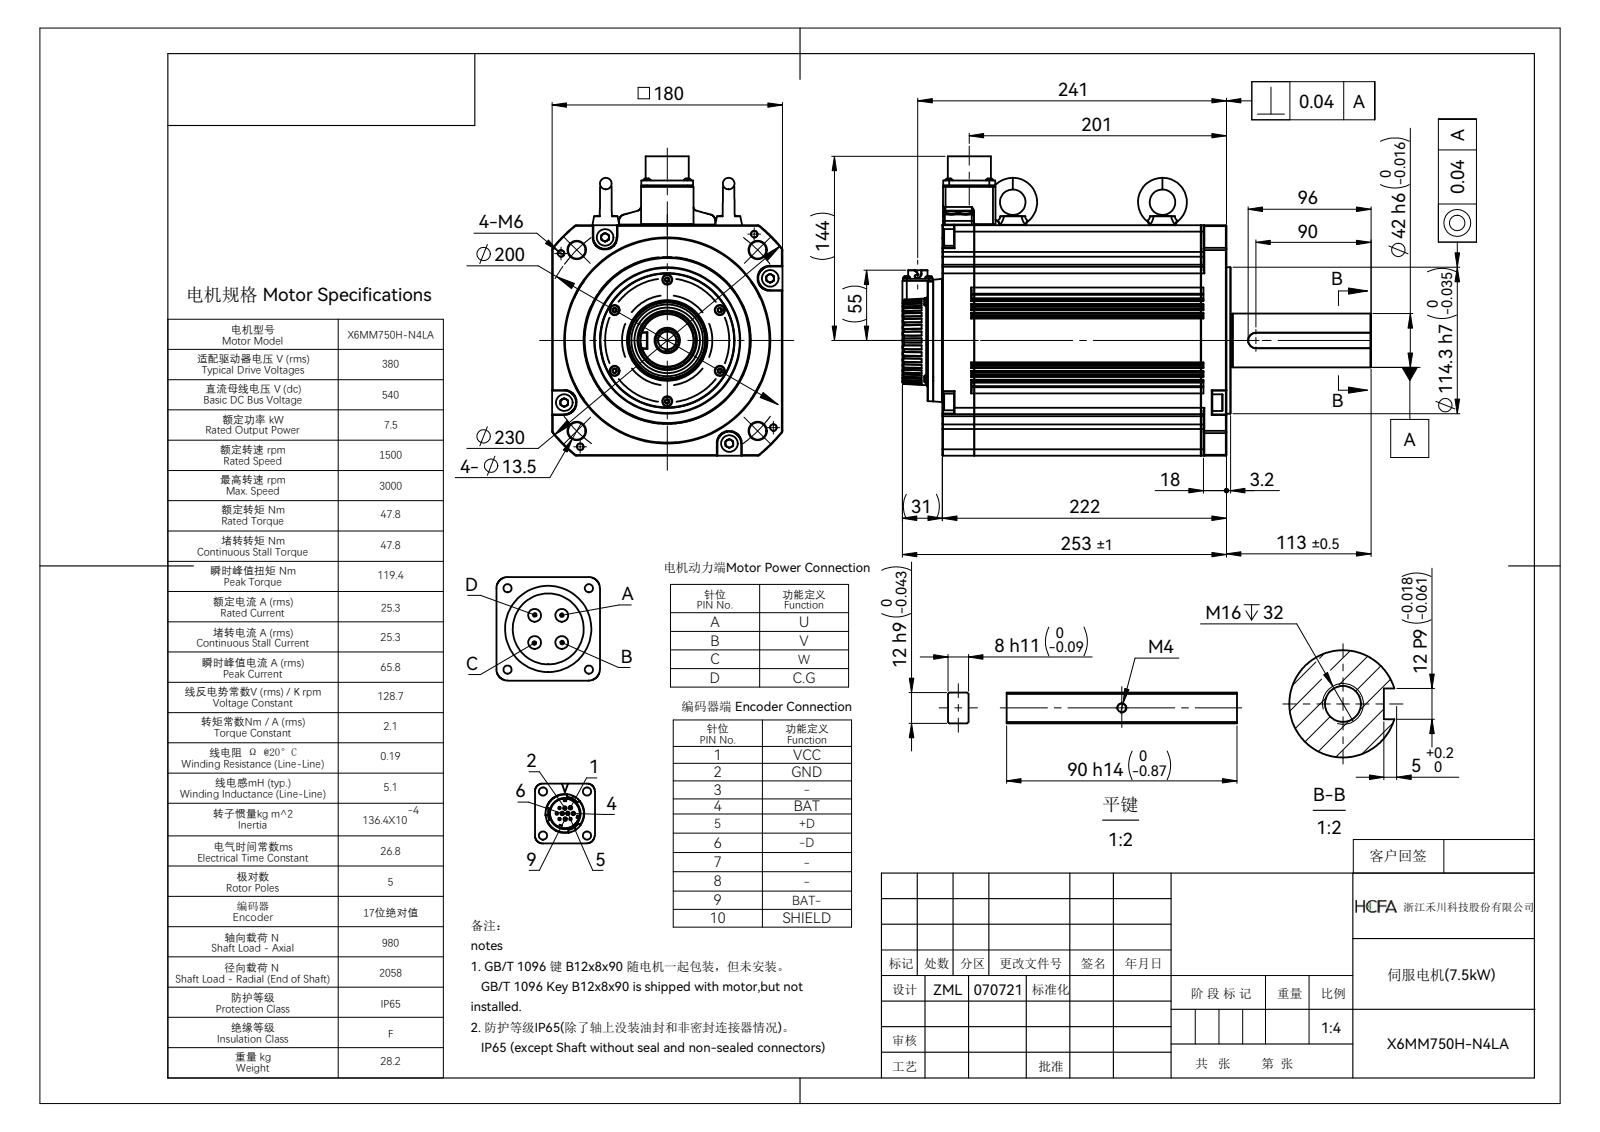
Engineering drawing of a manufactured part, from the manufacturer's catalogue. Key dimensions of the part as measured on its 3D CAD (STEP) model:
Part name (STEP PRODUCT): SV-X6MM750H-N4LA
STEP written by: SolidWorks 2016 (CONFIG_CONTROL_DESIGN)
Units: millimetres
Bodies: 1 solid, 2223 faces (763 planar, 831 cylindrical, 629 other)
Overall size (bounding box): 366.2 × 233.9 × 180
Volume: 6 642 000 mm³ · Surface area: 297 222 mm²
Round holes (diameter × count): ⌀13.5 ×4, ⌀2.5 ×2, ⌀11.6 ×1, ⌀11.8 ×1, ⌀14 ×1, ⌀27.7 ×1
Round bosses / shafts (diameter × count): ⌀1 ×10, ⌀13 ×6, ⌀7 ×4, ⌀6.7 ×4, ⌀5.7 ×4, ⌀5 ×4, ⌀0.8 ×4, ⌀2.4 ×2
Partial cylindrical surfaces — rounded edges, fillets, slot ends (radius × count): R0.5 ×84, R0.15 ×48, R1.5 ×47, R1 ×40, R0.2 ×32, R5 ×24, R0.55 ×16, R2 ×16
Main face-to-face distances: 180, 32.5, 147.5, 115, 222, 225.2, 3.2, 6.97, 51.96, 4
Hole centre spacings: 100, 141.42, 12.16, 49.55, 200, 17.2, 40.2
